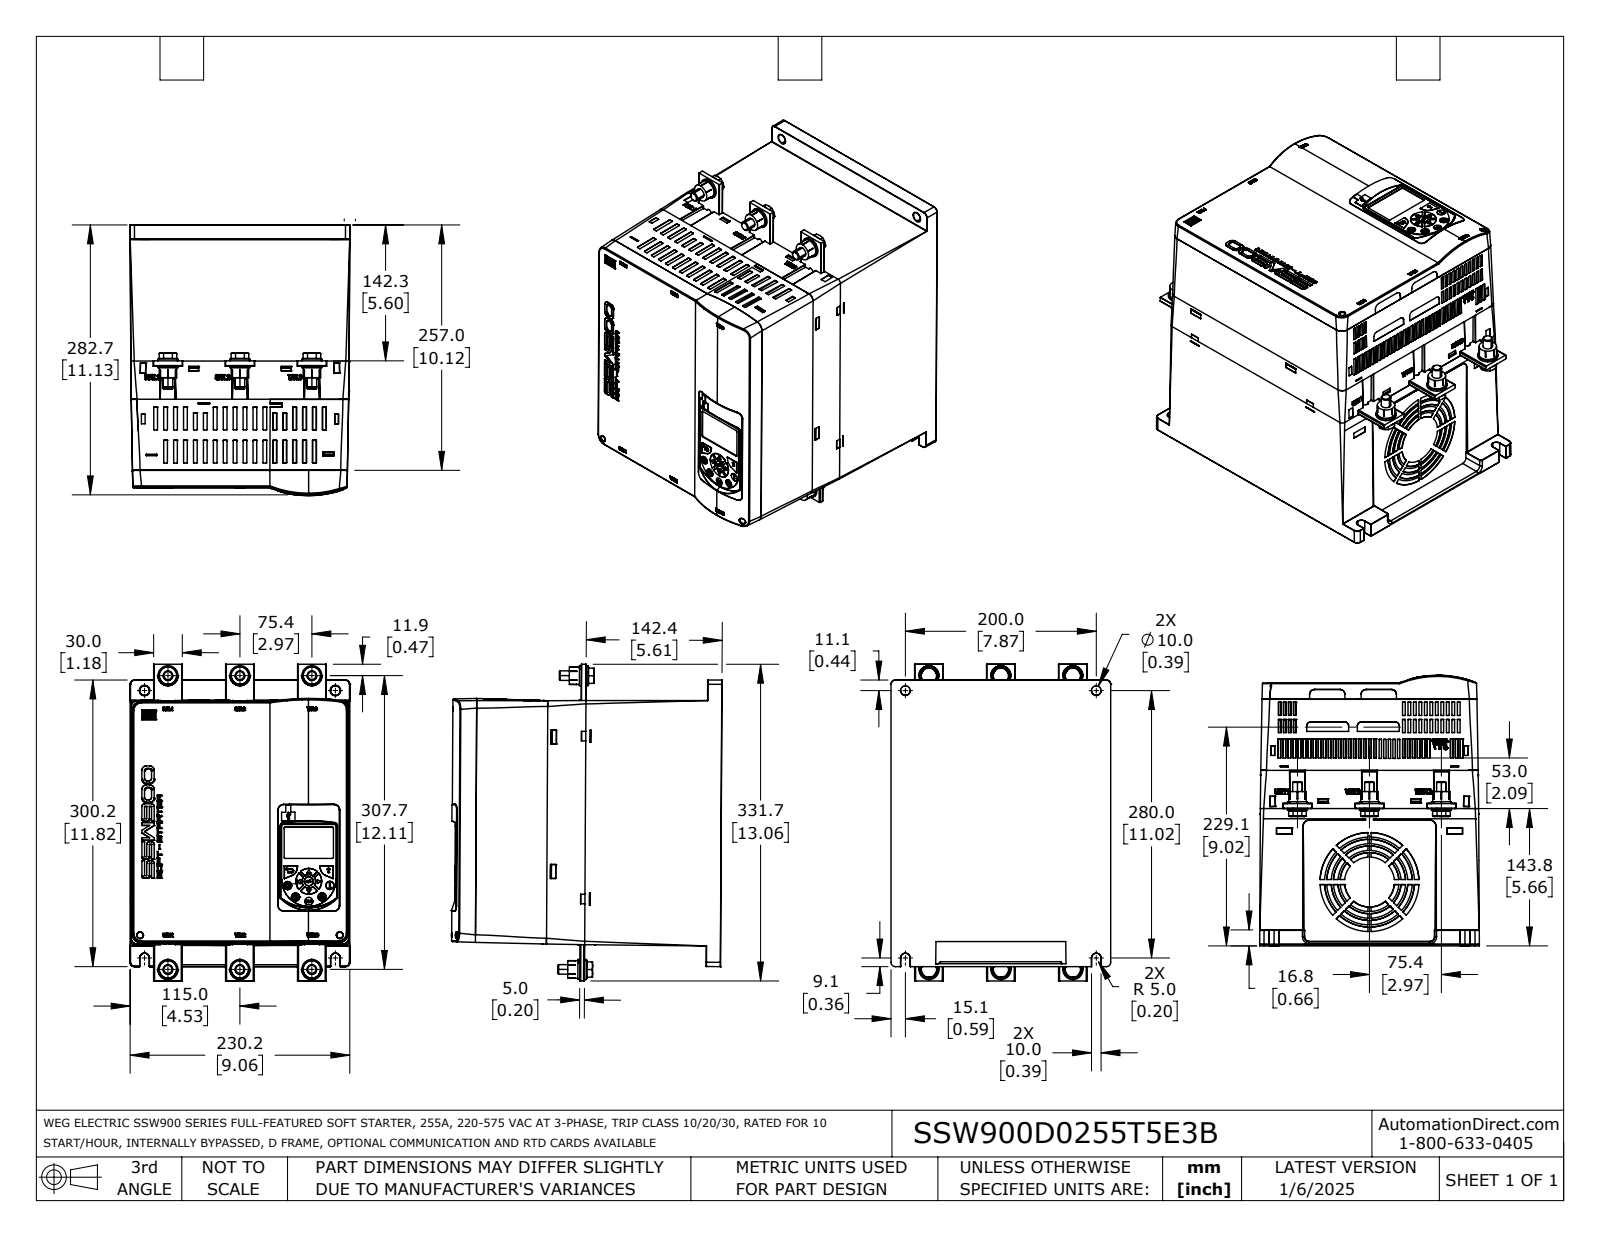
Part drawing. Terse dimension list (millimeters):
name: SSW900D0255T5E3B
written by: SolidWorks 2021 (AUTOMOTIVE_DESIGN)
unit: mm
bodies: 1 solid, 4211 faces (2804 planar, 500 cylindrical, 907 other)
size: 331.7 × 283.5 × 230.1
volume: 2 838 000 mm³; area: 813 500 mm²
holes: 2× ⌀10, 1× ⌀3.4, 1× ⌀6.6, 1× ⌀61.7, 1× ⌀75.7, 1× ⌀89.7, 1× ⌀103.7
bosses: 9× ⌀21, 6× ⌀18.3, 6× ⌀10, 1× ⌀94.3, 1× ⌀80.3, 1× ⌀66.3, 1× ⌀3.8, 1× ⌀1.4
rounds: 103× R0.3, 24× R0.5, 22× R0.4, 22× R0.5, 20× R0.5, 17× R1, 7× R0.2, 6× R2
face distances: 17.9, 248.4, 274.2, 256.3, 2.5, 17.2, 257, 239.1, 14.8, 271.7
hole spacings: 200, 257.6, 328.9
